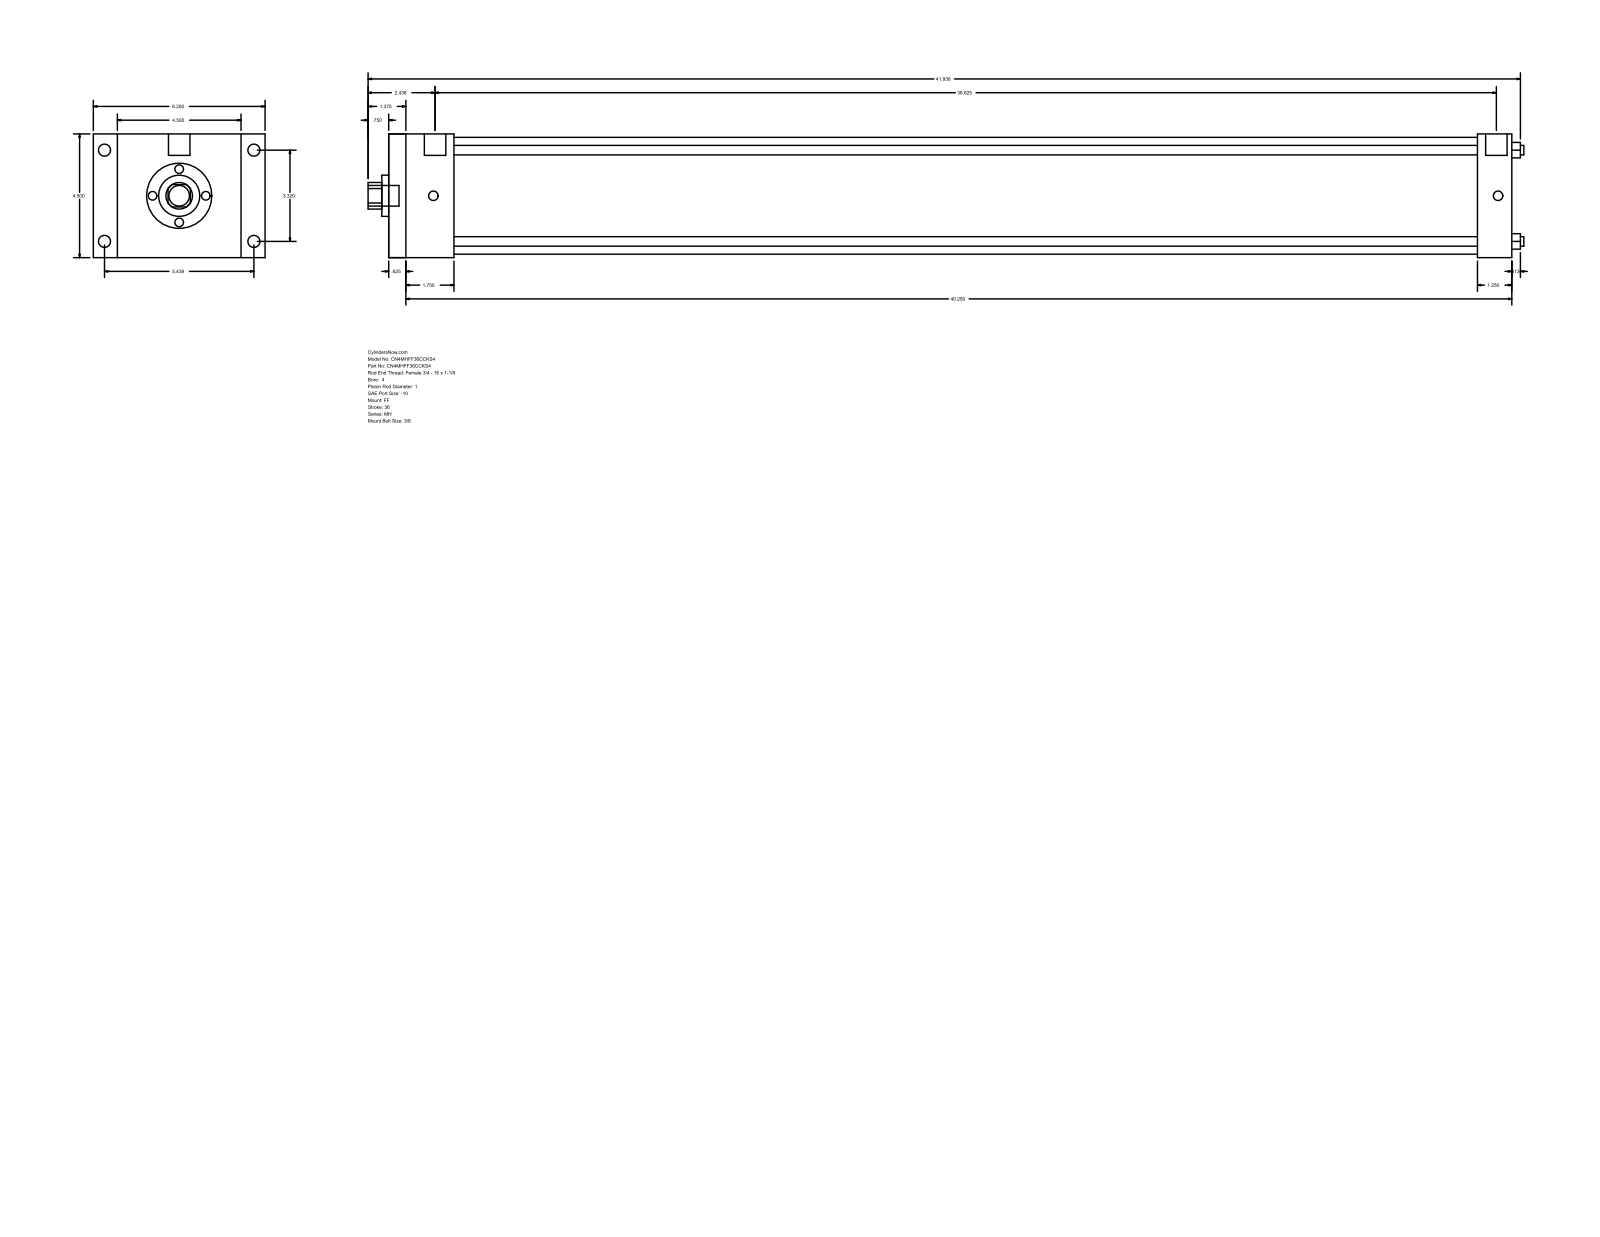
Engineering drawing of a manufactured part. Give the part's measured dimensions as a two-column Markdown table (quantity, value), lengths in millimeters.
| quantity | value |
| --- | --- |
| part name | MH_FF__0400_1 |
| STEP written by | GSSL Pune (CONFIG_CONTROL_DESIGN) |
| units | millimeters |
| bodies | 0 solids, 92 faces (64 planar, 28 cylindrical, 0 other) |
| overall size | 1068.39 × 158.75 × 114.3 |
| round holes (diameter × count) | 8.76 × 4, 25.4 × 1, 38.1 × 1, 107.95 × 1 |
| round bosses / shafts (diameter × count) | 11.13 × 4, 8.73 × 4, 19.84 × 2, 19.05 × 1 |
| partial cylindrical surfaces (radius × count) | 12.29 × 1 |
| main face-to-face distances | 114.3, 1038.23, 15.87, 1022.36, 60.33, 44.46, 977.9, 1006.48, 990.61, 946.15 |
| hole center spacings | 59.62, 84.32, 119.25 |
